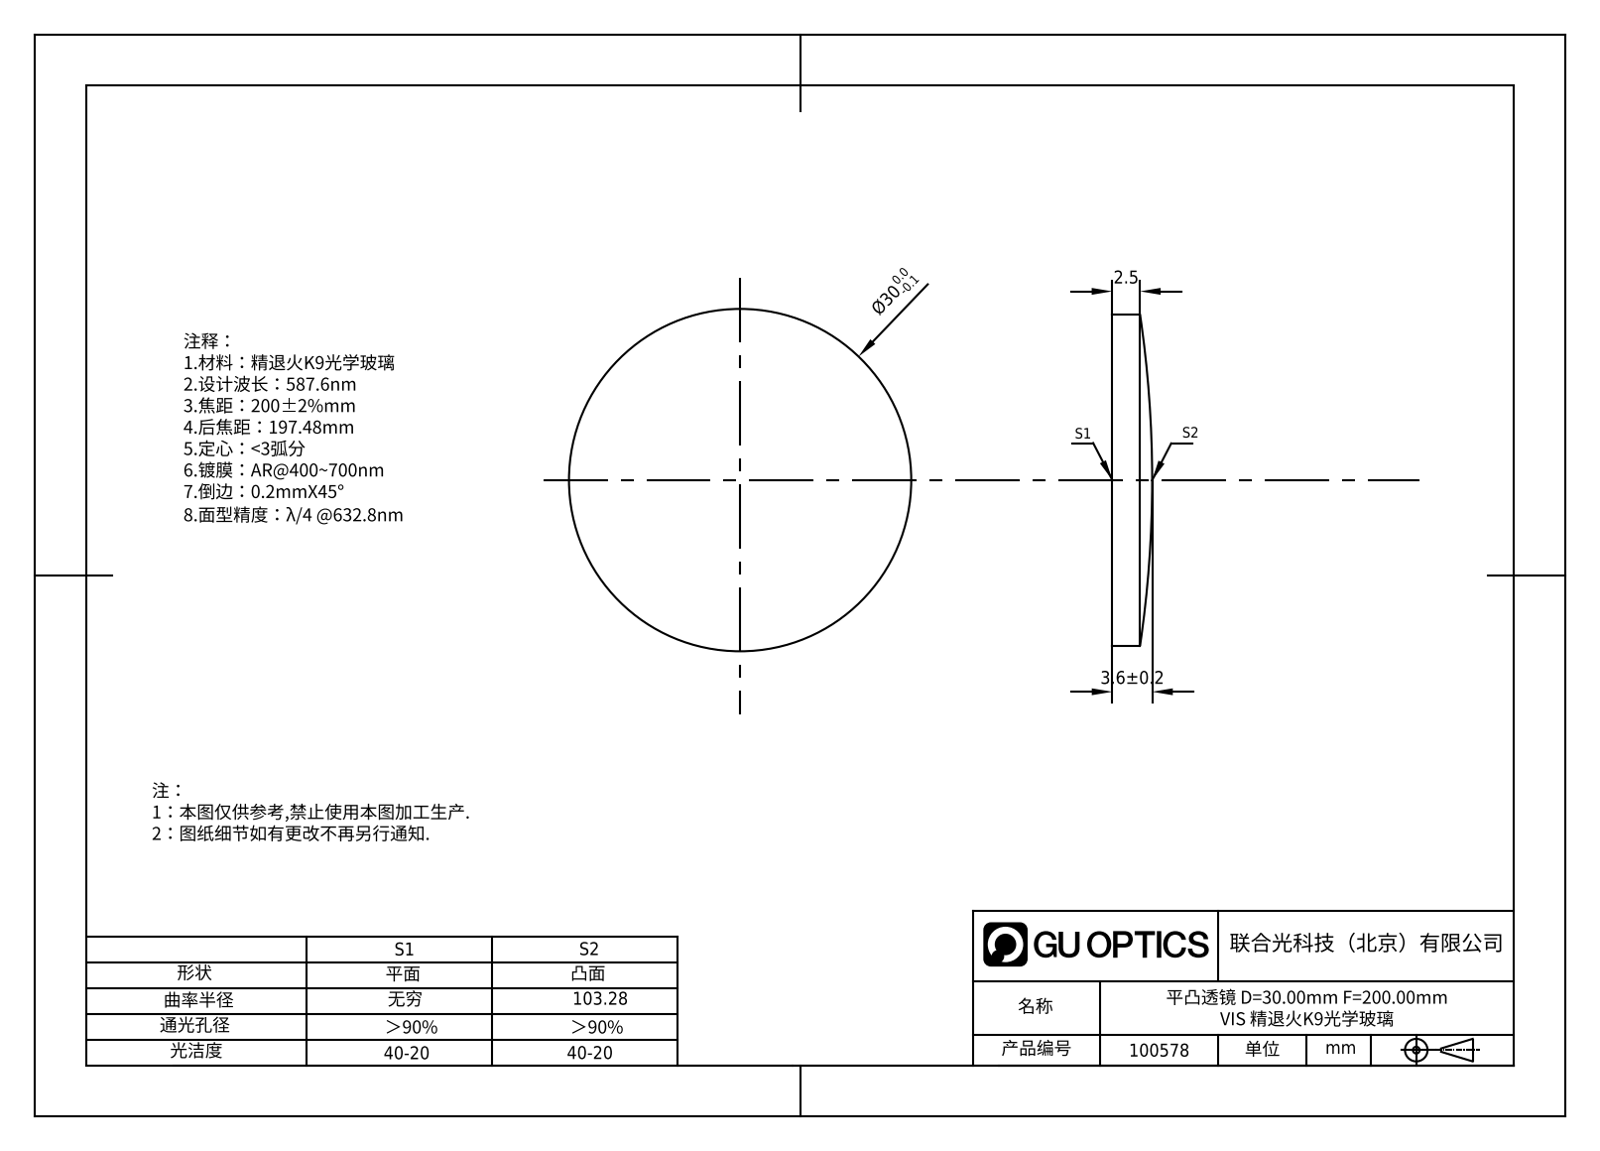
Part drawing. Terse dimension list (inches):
name: 100578
written by: SolidWorks 2020 (CONFIG_CONTROL_DESIGN)
unit: in
bodies: 1 solid, 5 faces (1 planar, 2 cylindrical, 2 other)
size: 1.181 × 1.181 × 0.142
volume: 0.132 in³; area: 2.562 in²
bosses: 1× ⌀1.181
